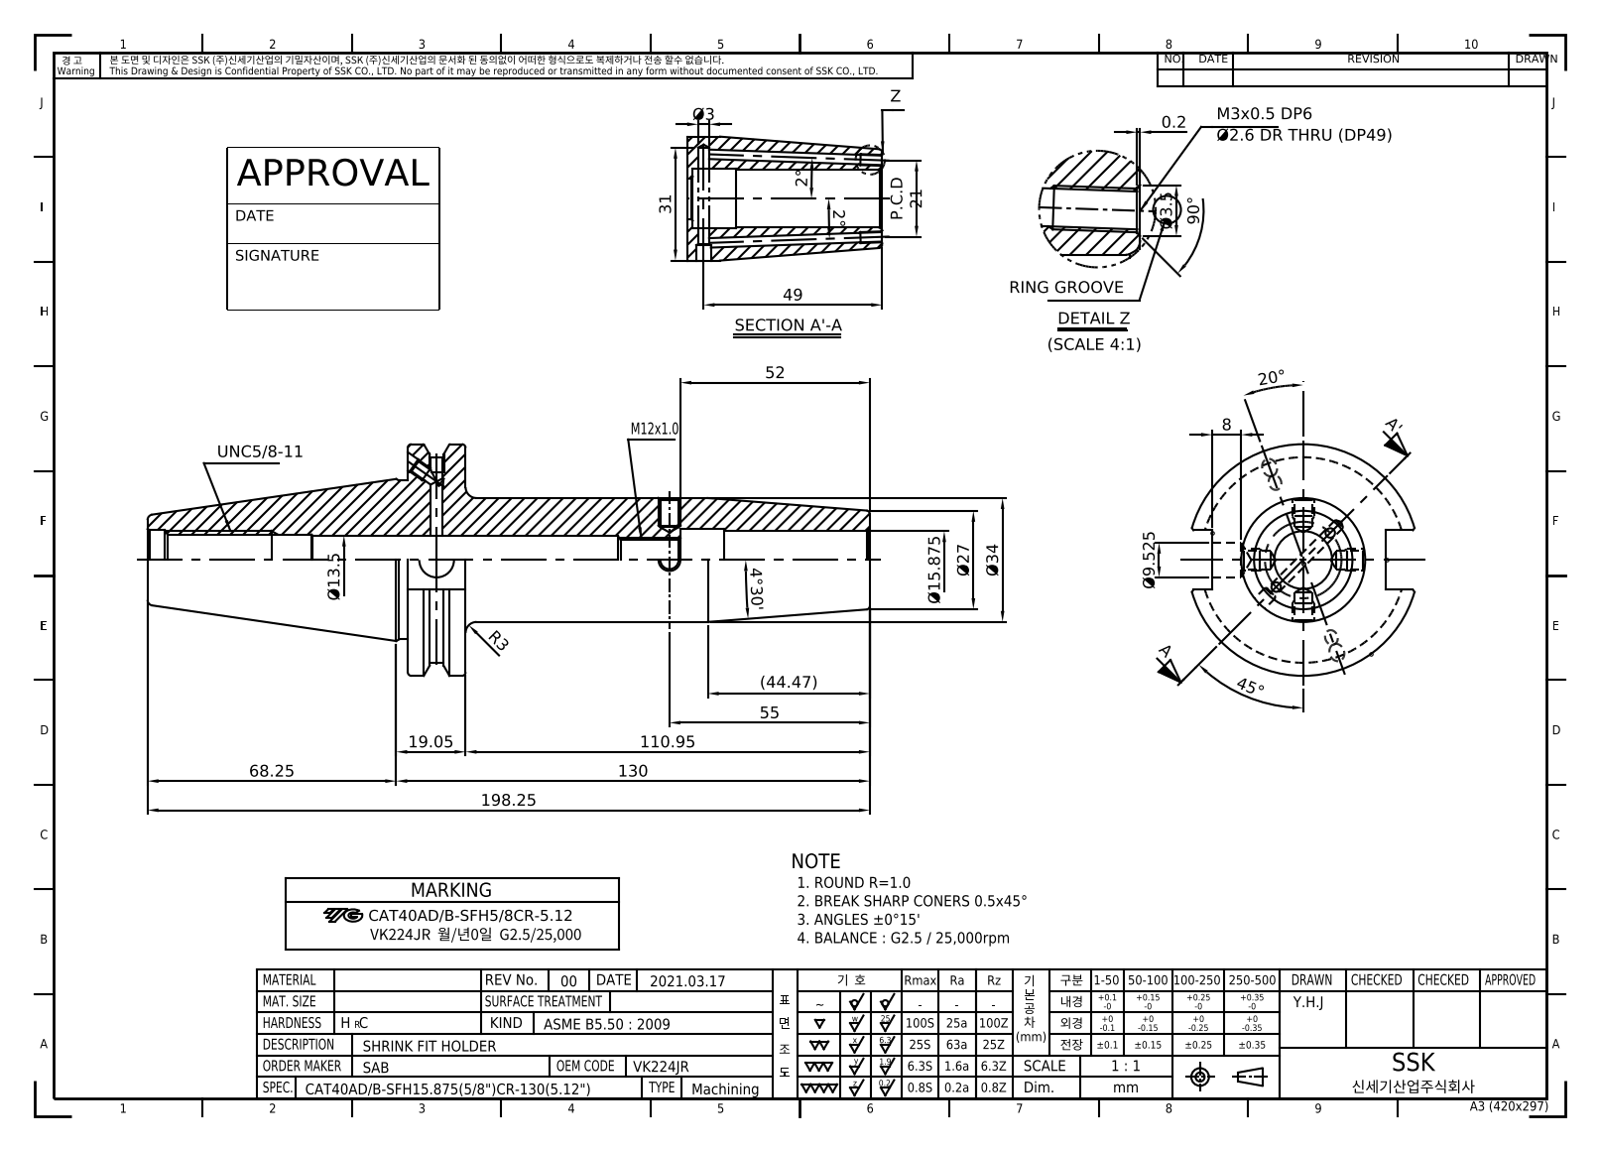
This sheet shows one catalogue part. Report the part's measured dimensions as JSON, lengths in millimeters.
{"part_name": "LO-CAT40ADB-SFH15.875CR-130", "step_written_by": "Autodesk Inventor 2022 (AUTOMOTIVE_DESIGN)", "units": "millimeters", "bodies": {"solids": 1, "faces": 91, "planar": 37, "cylindrical": 31, "other": 23}, "overall_size": [198.25, 63.5, 61.09], "volume_mm3": 175692, "surface_area_mm2": 37325, "round_holes": [[3.24, 4], [2.46, 2], [4, 2], [4.2, 2], [9.53, 1], [10.92, 1], [13, 1], [13.39, 1], [15.88, 1], [16.3, 1], [17, 1]], "round_bosses_or_shafts": [[63.5, 1], [43.6, 1], [34, 1]], "partial_cylinders_radius": [[28.15, 1]], "face_to_face_distances": [15.88, 126.83, 110.95, 47.6, 16.38, 71.42, 87.3, 198.25, 146.25, 74.83]}
